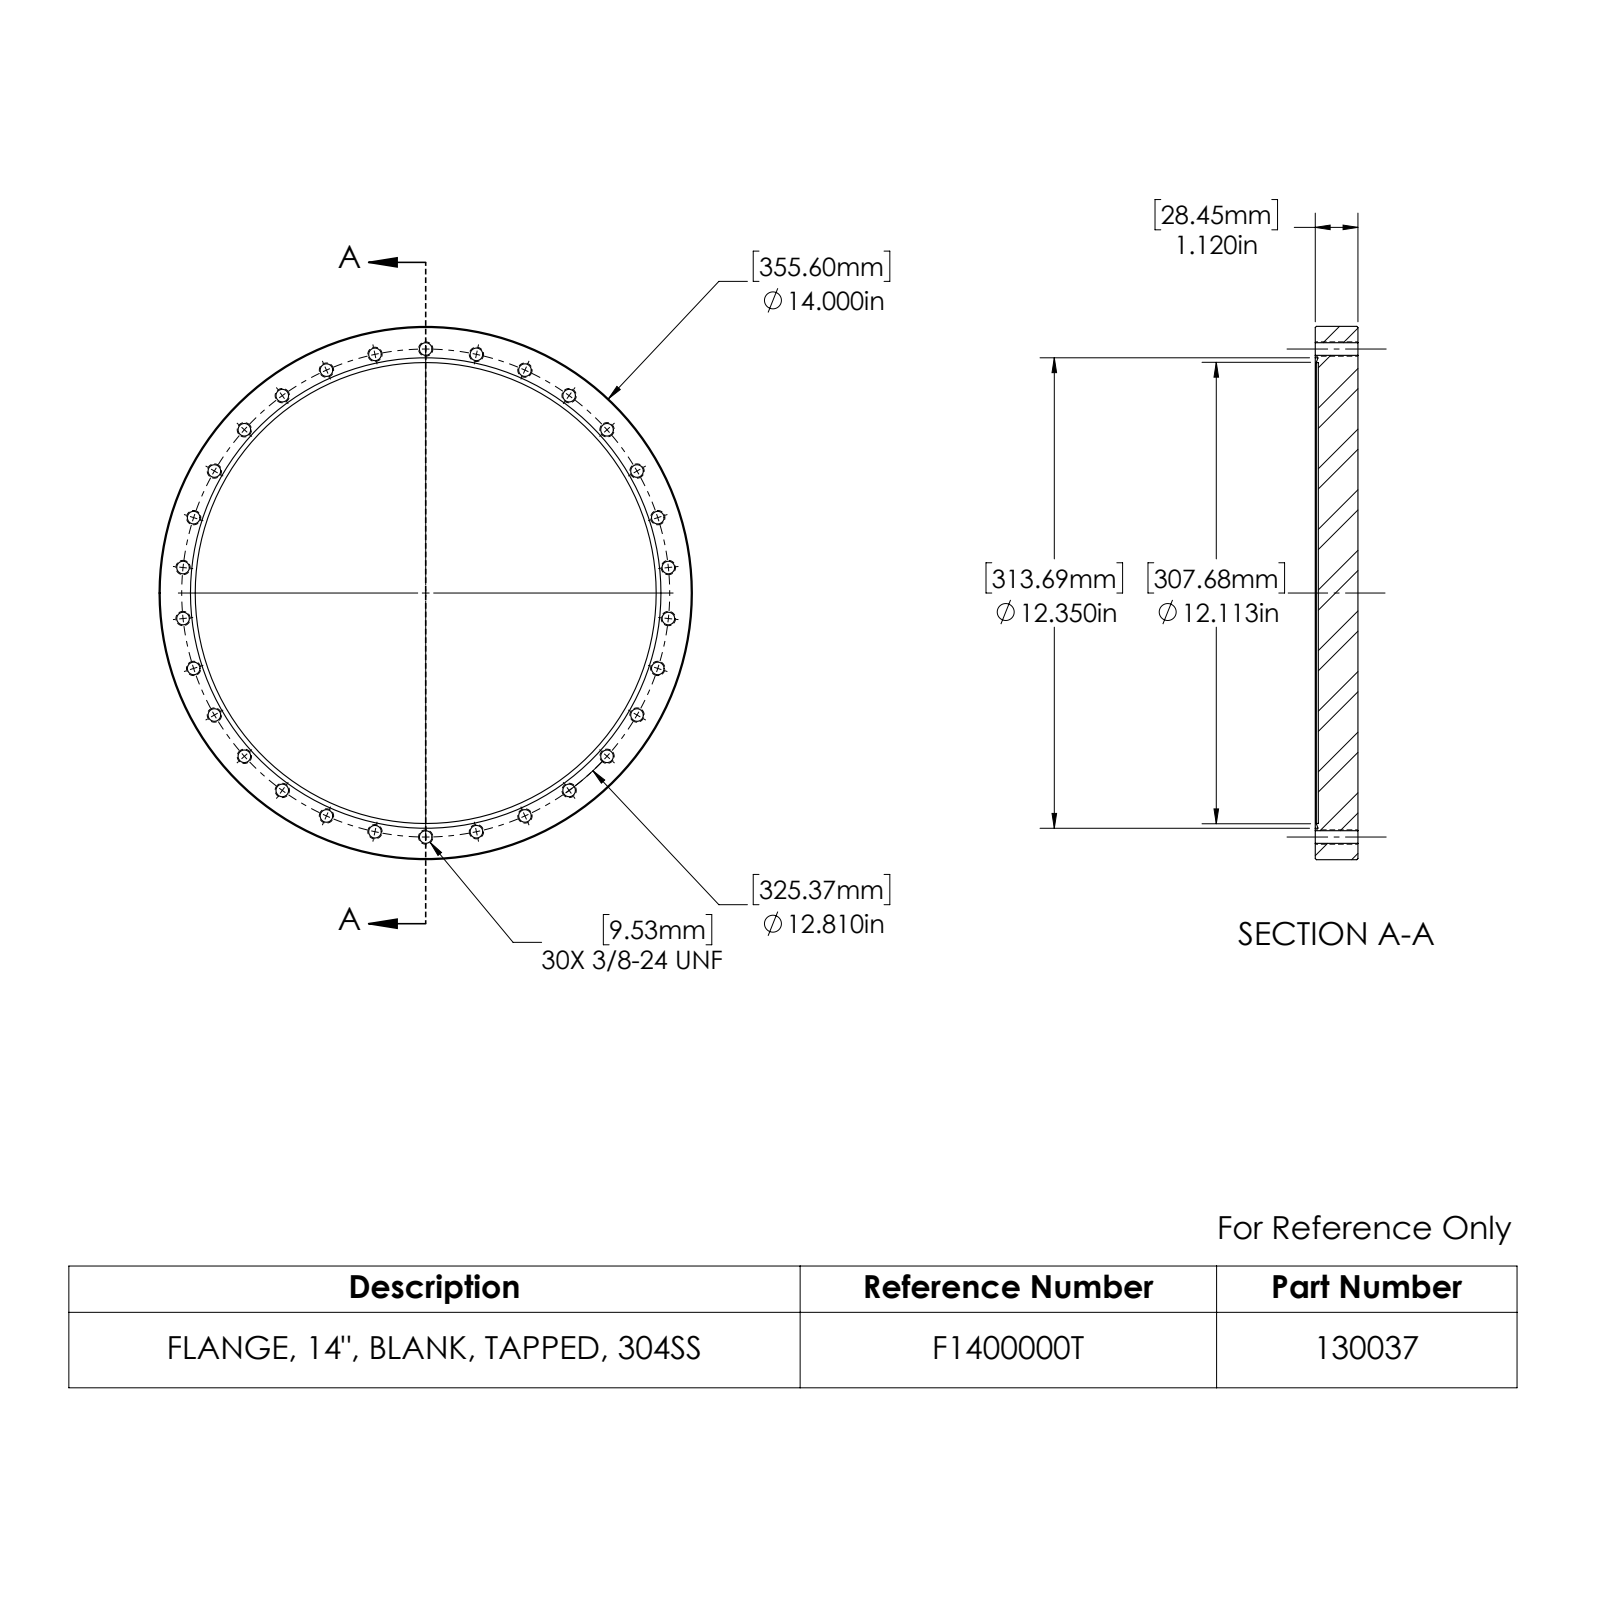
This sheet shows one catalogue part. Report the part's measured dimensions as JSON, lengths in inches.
{"part_name": "130037_C", "step_written_by": "SolidWorks 2022 (CONFIG_CONTROL_DESIGN)", "units": "inches", "bodies": {"solids": 1, "faces": 81, "planar": 3, "cylindrical": 66, "other": 12}, "overall_size": [14, 14, 1.12], "volume_in3": 160, "surface_area_in2": 390.1, "round_holes": [[0.332, 30], [12.1, 1], [12.35, 1]], "round_bosses_or_shafts": [[14, 1]], "face_to_face_distances": [1.04, 0.08, 1.12], "hole_center_spacings": [1.339, 7.53, 10.363, 2.663, 3.959, 12.74, 5.21, 8.572]}
